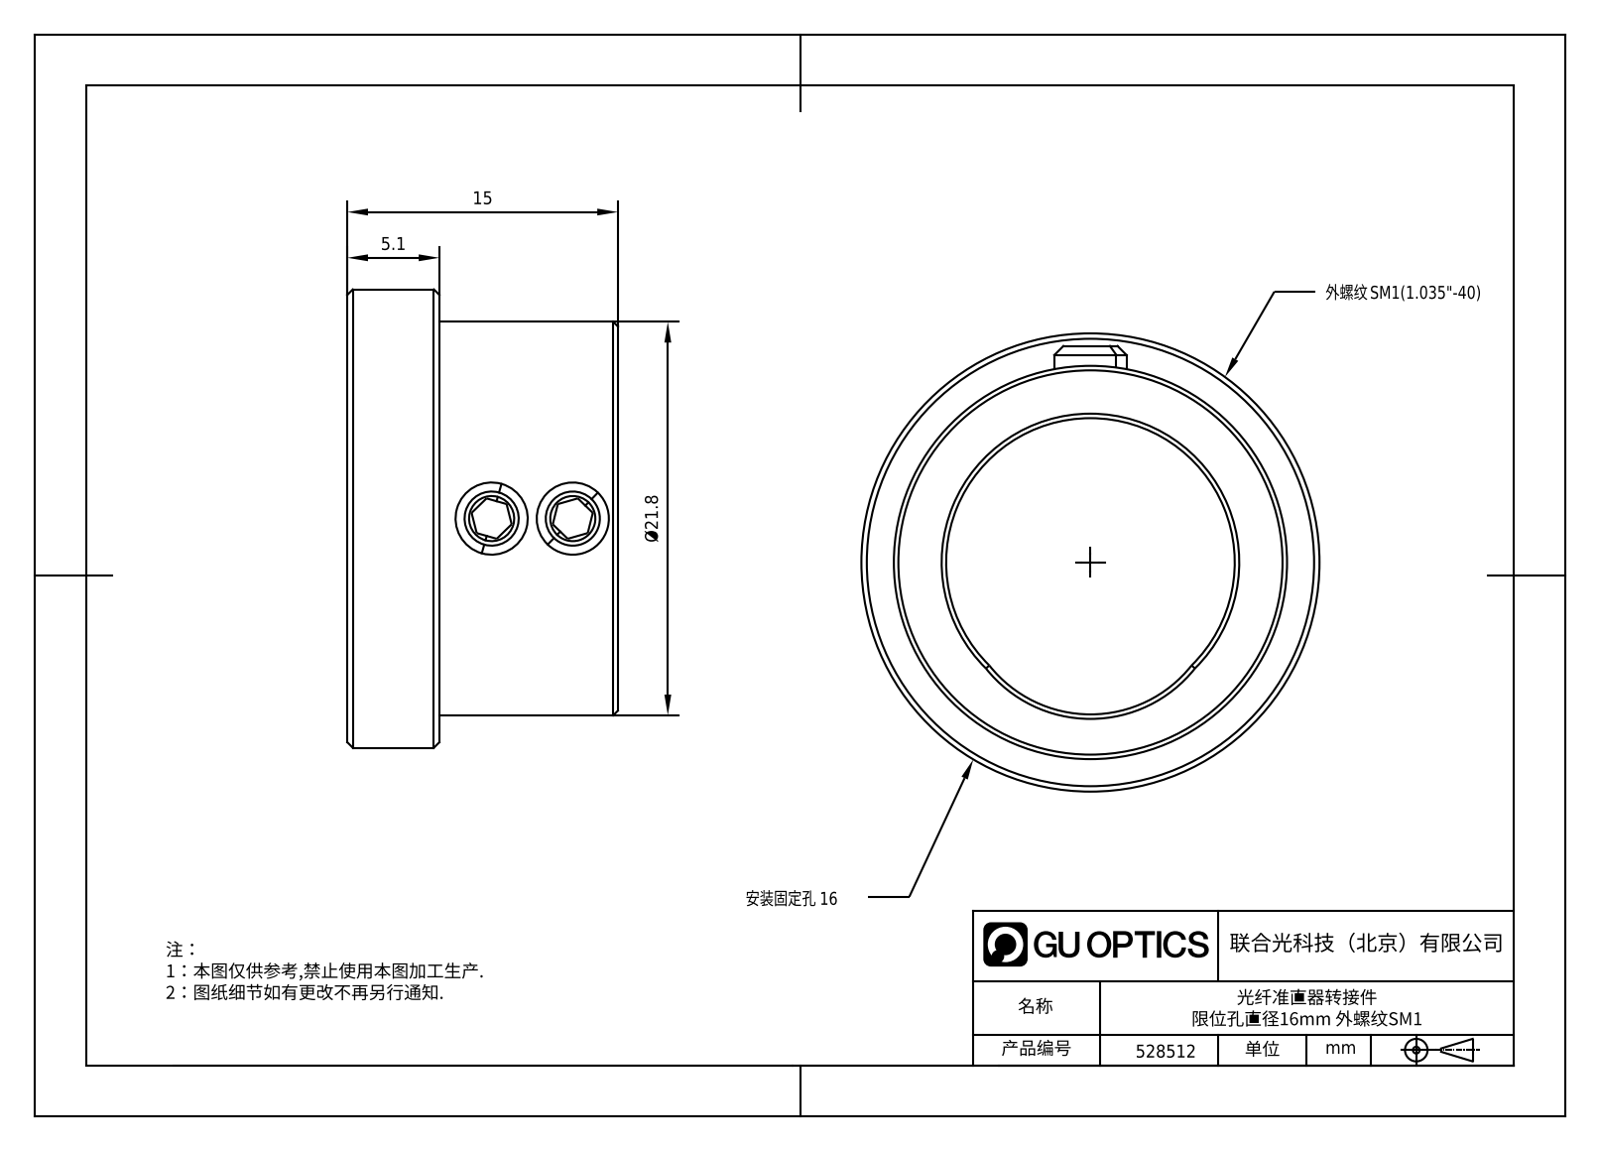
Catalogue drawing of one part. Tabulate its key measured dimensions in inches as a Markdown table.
| quantity | value |
| --- | --- |
| part name | 30.8.8-14，M4尼龙头顶丝，A_30.8.56-LNJ4*3 |
| STEP written by | SolidWorks 2021 (CONFIG_CONTROL_DESIGN) |
| units | inches |
| bodies | 3 solids, 85 faces (27 planar, 28 cylindrical, 30 other) |
| overall size | 1 × 1 × 0.591 |
| volume | 0.196 in³ |
| surface area | 4.008 in² |
| round holes (diameter × count) | 0.05 × 2, 0.13 × 2 |
| round bosses / shafts (diameter × count) | 0.157 × 2, 0.118 × 2, 1 × 1, 0.858 × 1 |
| partial cylindrical surfaces (radius × count) | 0.281 × 1, 0.315 × 1 |
| main face-to-face distances | 0.591, 0.201, 0.39, 0.118, 0.05, 0.151, 0.079, 0.157, 0.039, 0.101 |
| hole center spacings | 0.177, 0.799 |
